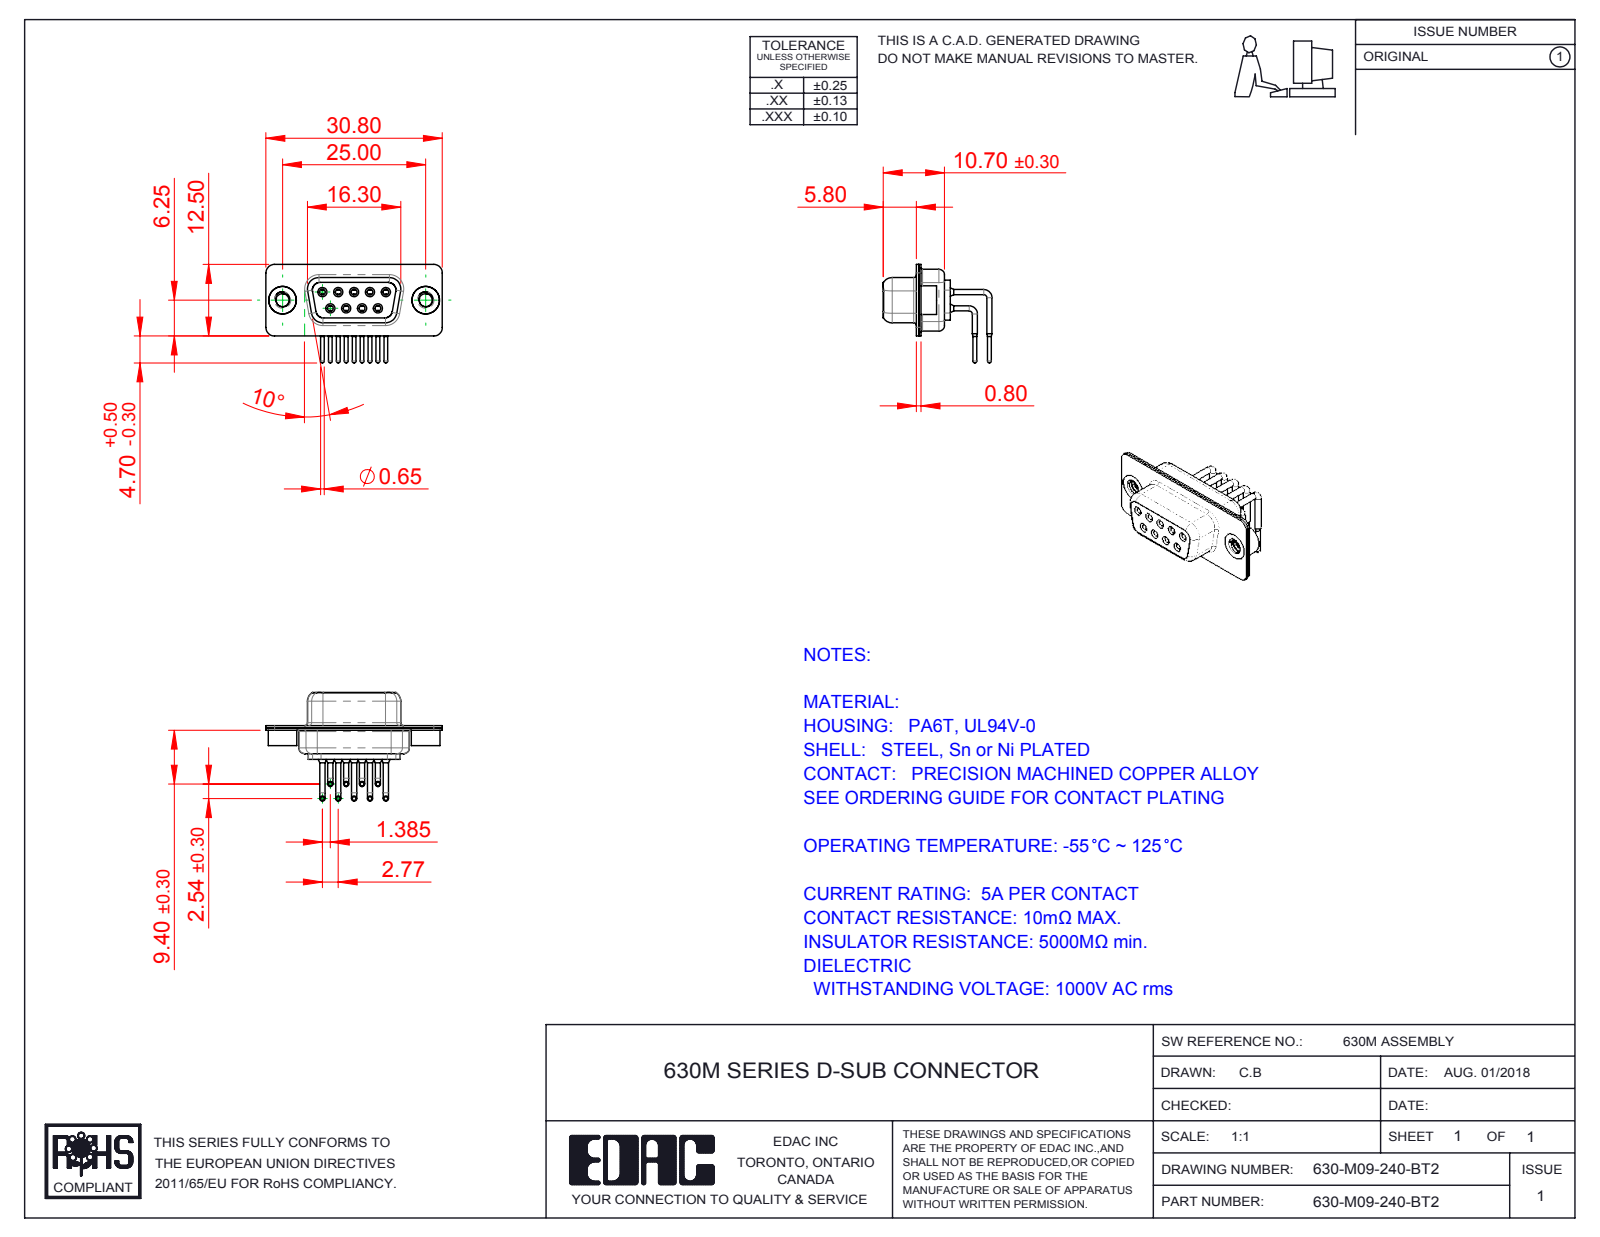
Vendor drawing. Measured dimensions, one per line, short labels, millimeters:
name: 630M Contact Row 2; 630M Contact Row 1; 630M Shell Rear_09 Contacts; 630M Shell Front_09 Contacts (+3 more)
written by: SolidWorks 2016 (CONFIG_CONTROL_DESIGN)
unit: mm
bodies: 14 solids, 756 faces (202 planar, 344 cylindrical, 210 other)
size: 30.8 × 18.99 × 17.2
volume: 1 761 mm³; area: 4 640 mm²
holes: 9× ⌀1, 9× ⌀1.1, 9× ⌀1.7, 9× ⌀1.8, 9× ⌀2, 2× ⌀2.26, 2× ⌀4, 2× ⌀4.8
bosses: 18× ⌀0.9, 9× ⌀1.6, 9× ⌀1.5, 9× ⌀0.65, 2× ⌀5, 2× ⌀4.9
rounds: 16× R1.5, 12× R2, 8× R1.35, 8× R1.6, 4× R0.25, 4× R0.5, 4× R0.6, 4× R0.65
face distances: 0.4, 0.8, 1.45, 2.3, 8.95, 6.2, 8.5, 1.9, 0.85, 9.35
hole spacings: 3.16, 2.77, 5.54, 5.03, 5.04, 8.31, 7.1, 7.48
